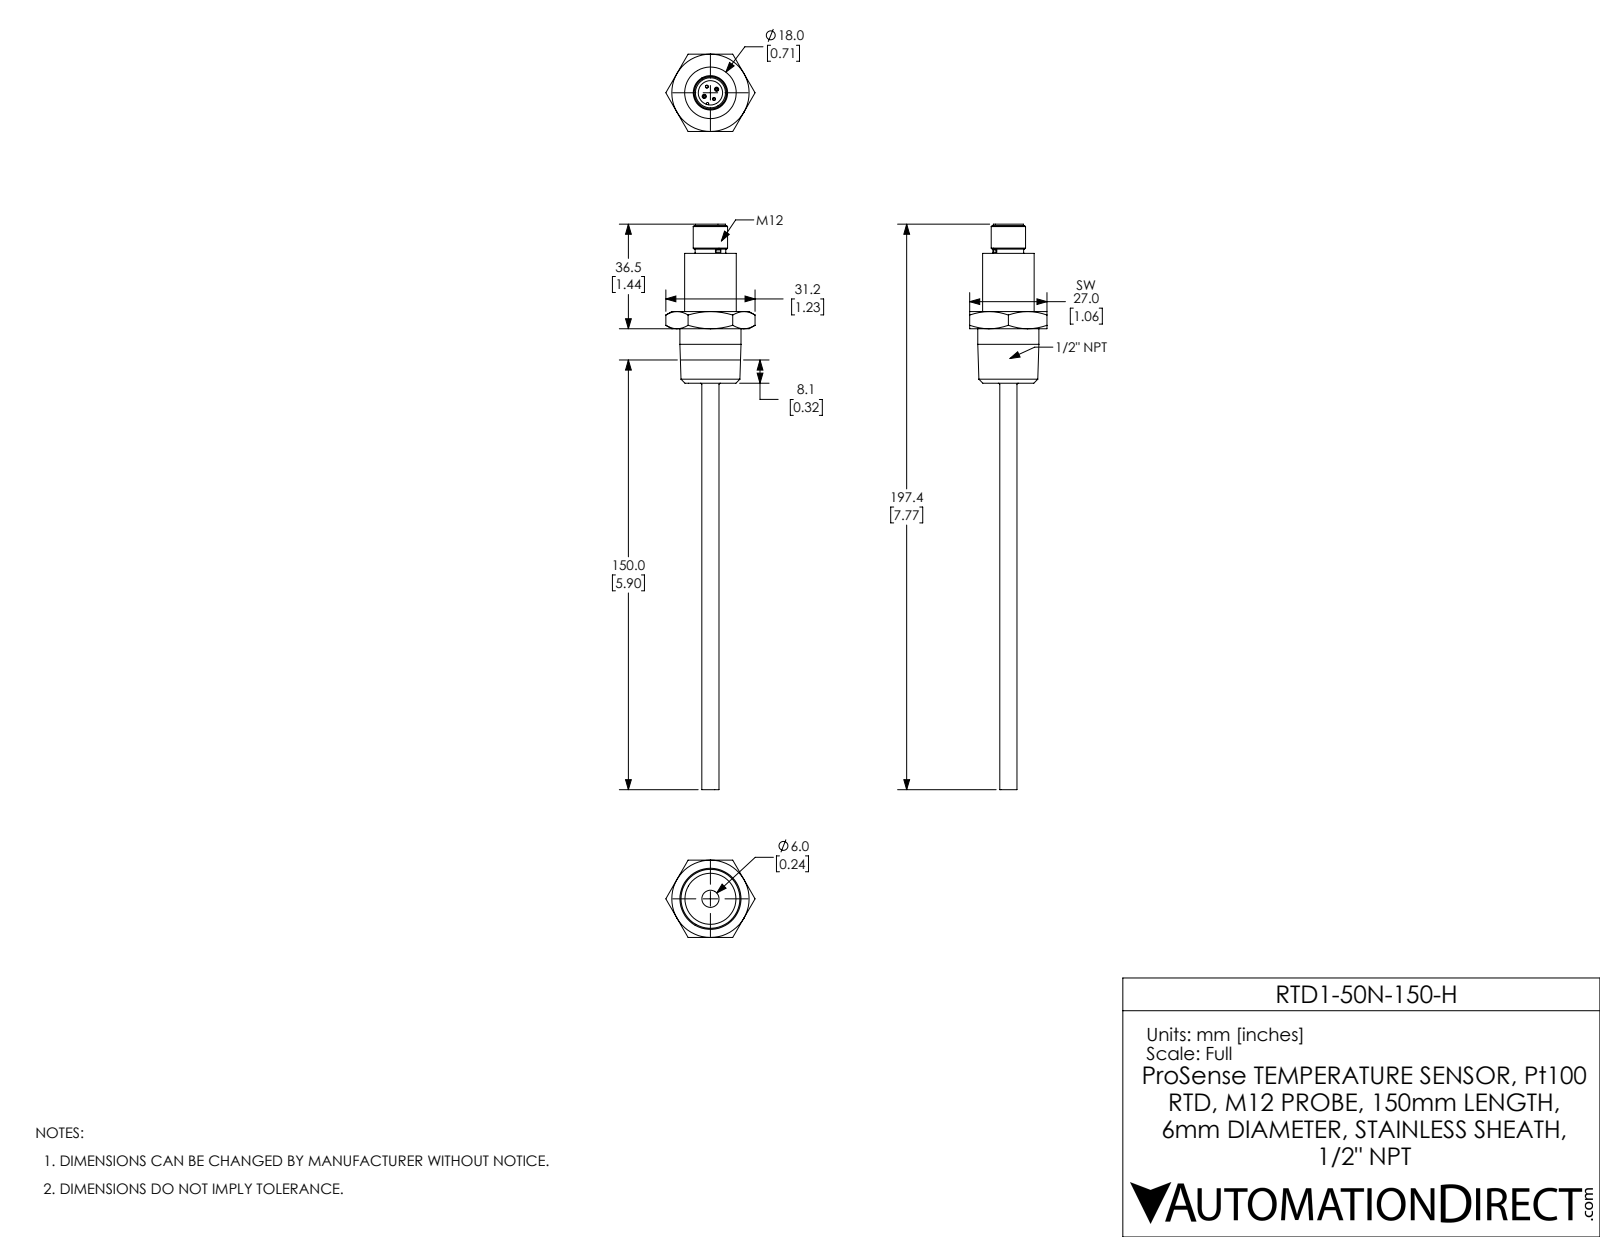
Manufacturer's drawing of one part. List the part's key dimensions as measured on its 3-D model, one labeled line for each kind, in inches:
Part name (STEP PRODUCT): RTD1-50N-150-H
STEP written by: SolidWorks 2017 (AUTOMOTIVE_DESIGN)
Units: inches
Bodies: 1 solid, 94 faces (32 planar, 23 cylindrical, 39 other)
Overall size (bounding box): 7.772 × 1.227 × 1.063
Volume: 1.225 in³ · Surface area: 11.57 in²
Round holes (diameter × count): ⌀0.335 ×1
Round bosses / shafts (diameter × count): ⌀0.04 ×4, ⌀0.84 ×1, ⌀0.709 ×1, ⌀0.472 ×1, ⌀0.421 ×1, ⌀0.413 ×1, ⌀0.236 ×1
Partial cylindrical surfaces — rounded edges, fillets, slot ends (radius × count): R0.016 ×1
Main face-to-face distances: 1.063, 0.236, 0.748, 0.984, 1.783, 1.035, 0.799, 1.831, 1.083, 0.846
